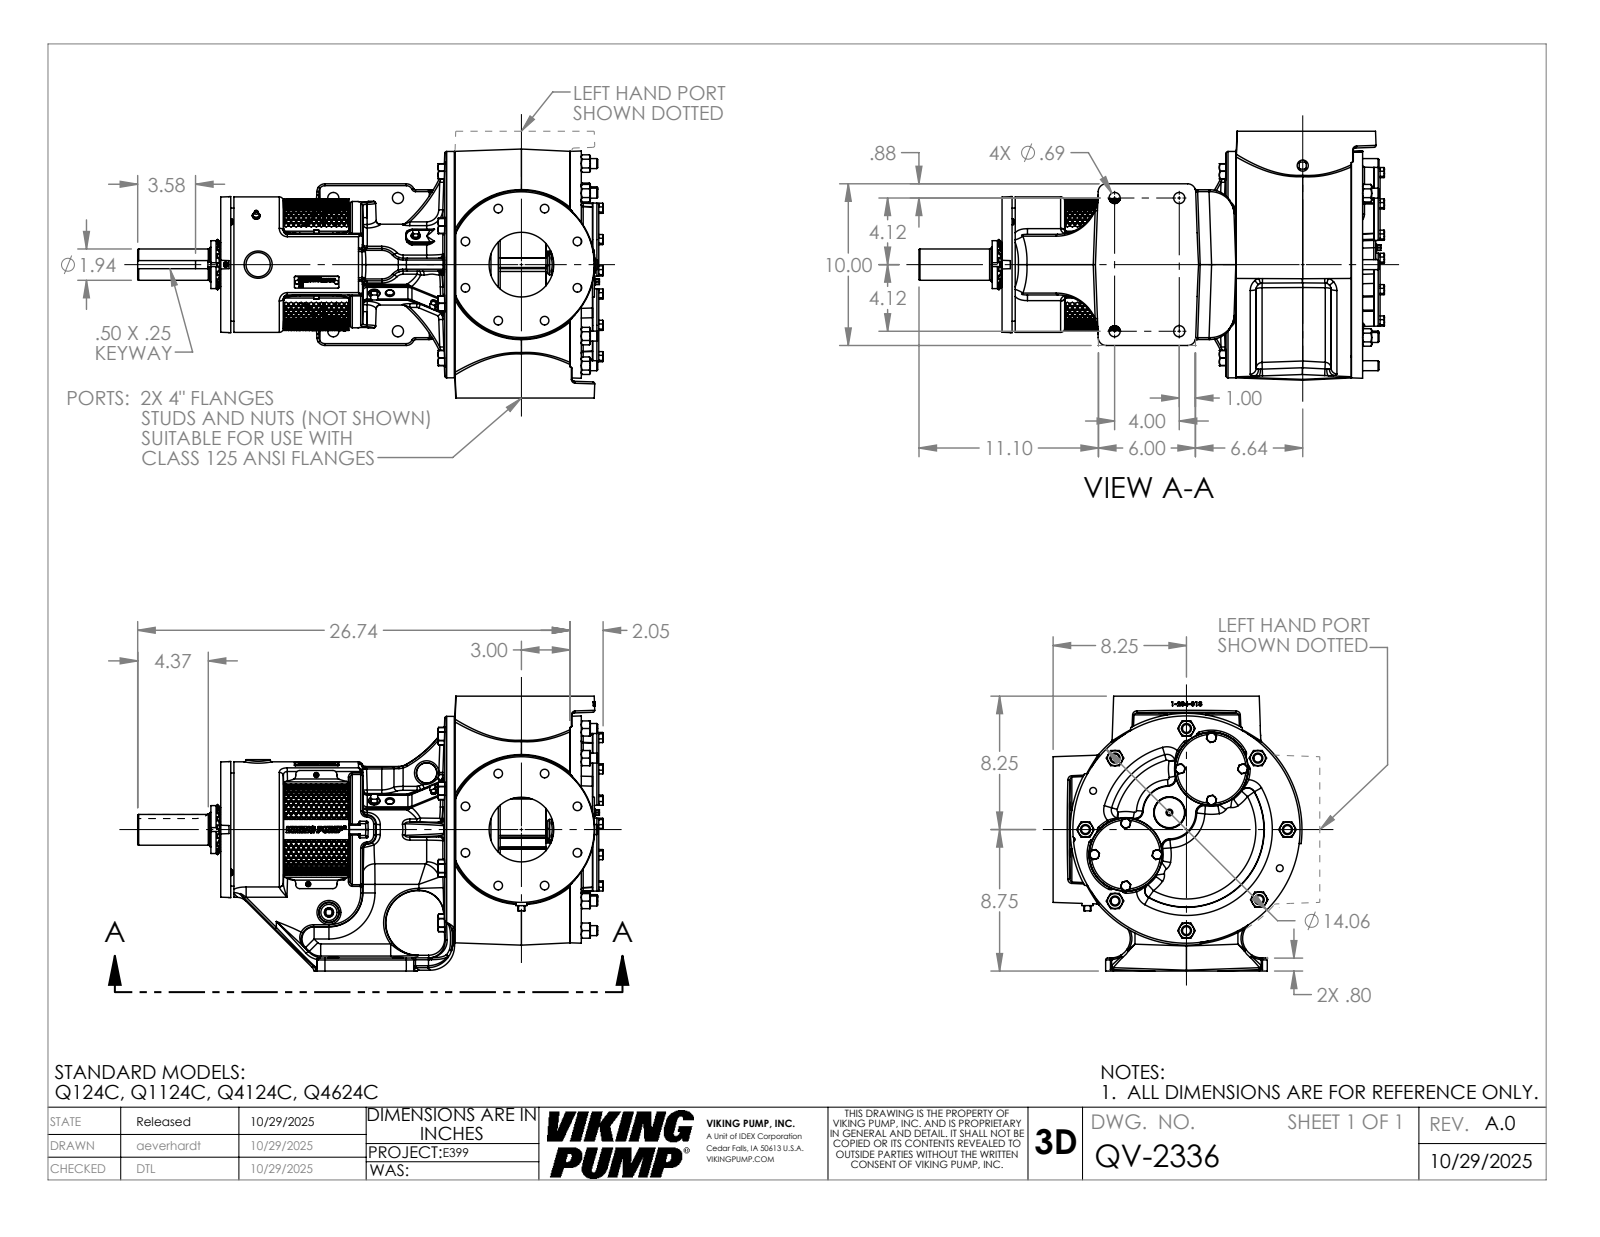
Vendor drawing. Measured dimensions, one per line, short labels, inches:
name: QV-2336
written by: SolidWorks 2024 (AUTOMOTIVE_DESIGN)
unit: in
bodies: 1 solid, 4003 faces (1383 planar, 605 cylindrical, 2015 other)
size: 28.797 × 19.12 × 17.519
volume: 2 033 in³; area: 2 070 in²
holes: 8× ⌀0.266, 8× ⌀1.157, 6× ⌀0.25, 4× ⌀0.531, 4× ⌀0.688, 2× ⌀0.159, 2× ⌀0.313, 2× ⌀0.422, 1× ⌀0.453, 1× ⌀2.157, 1× ⌀2.167, 1× ⌀2.182
bosses: 24× ⌀0.617, 14× ⌀0.625, 4× ⌀0.312, 3× ⌀0.437, 2× ⌀4.5, 2× ⌀0.625, 2× ⌀0.375, 1× ⌀14
rounds: 62× R0.12, 21× R0.25, 18× R0.015, 18× R0.092, 16× R0.07, 14× R0.75, 13× R0.5, 8× R0.06
face distances: 17, 22.31, 1.25, 3.82, 18.49, 23.391, 19.57, 1.081, 7.965, 4.145
hole spacings: 3.75, 2.079, 5.783, 2.713, 3.133, 3.788, 5.423, 5.932
